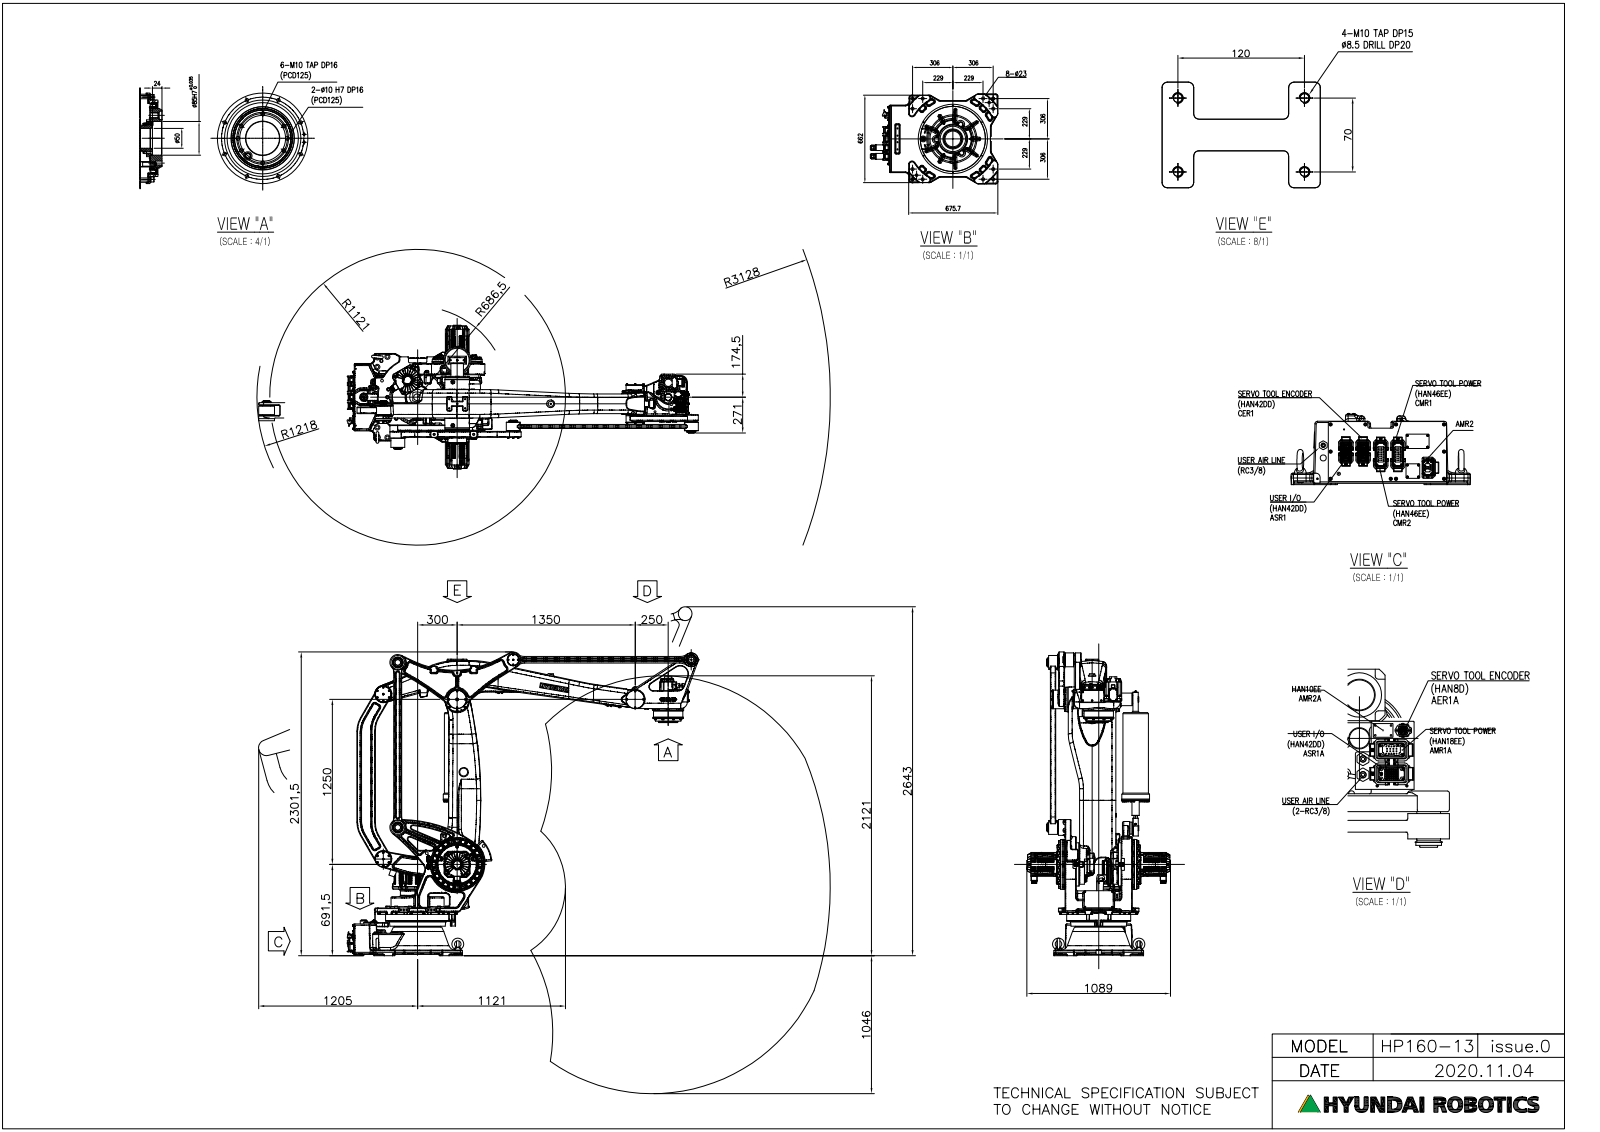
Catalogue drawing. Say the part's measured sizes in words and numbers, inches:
The part is named "lower frame assy; C-FLDZM; hp160-13; base body (+8 more)". Its 3-D file was written by "SolidWorks 2020 (CONFIG_CONTROL_DESIGN)". It is 71 solids with 11524 faces: 4383 planar, 3779 cylindrical and 3362 other. Overall it measures 102.341 by 96.701 by 43.425 inches. Its volume is 22 410 cubic inches and its surface area 23 850 square inches. Round holes: 12 of diameter 0.268, 9 of diameter 0.315, 9 of diameter 1.575, 8 of diameter 0.11, 8 of diameter 0.147, 8 of diameter 0.335, 8 of diameter 0.413, 8 of diameter 0.906, 6 of diameter 0.472, 6 of diameter 1.772, 5 of diameter 0.945, 4 of diameter 0.067. Round bosses or shafts: 46 of diameter 0.01, 12 of diameter 0.236, 12 of diameter 0.217, 9 of diameter 2.362, 8 of diameter 0.65, 8 of diameter 0.63, 8 of diameter 0.531, 8 of diameter 0.512. Partial cylindrical surfaces (rounded edges, fillets, slot ends): 303 of radius 0.039, 132 of radius 0.059, 106 of radius 0.394, 88 of radius 0.197, 79 of radius 0.118, 60 of radius 0.591, 54 of radius 0.02, 40 of radius 0.079. The main face-to-face distances are 1.181, 12.5, 1.929, 1.299, 0.591, 4.646, 0.157, 7.205, 0.669, 4.626. The hole center spacings are 0.972, 1.375, 2.993, 15.047, 21.024, 21.28, 24.241, 31.948.
